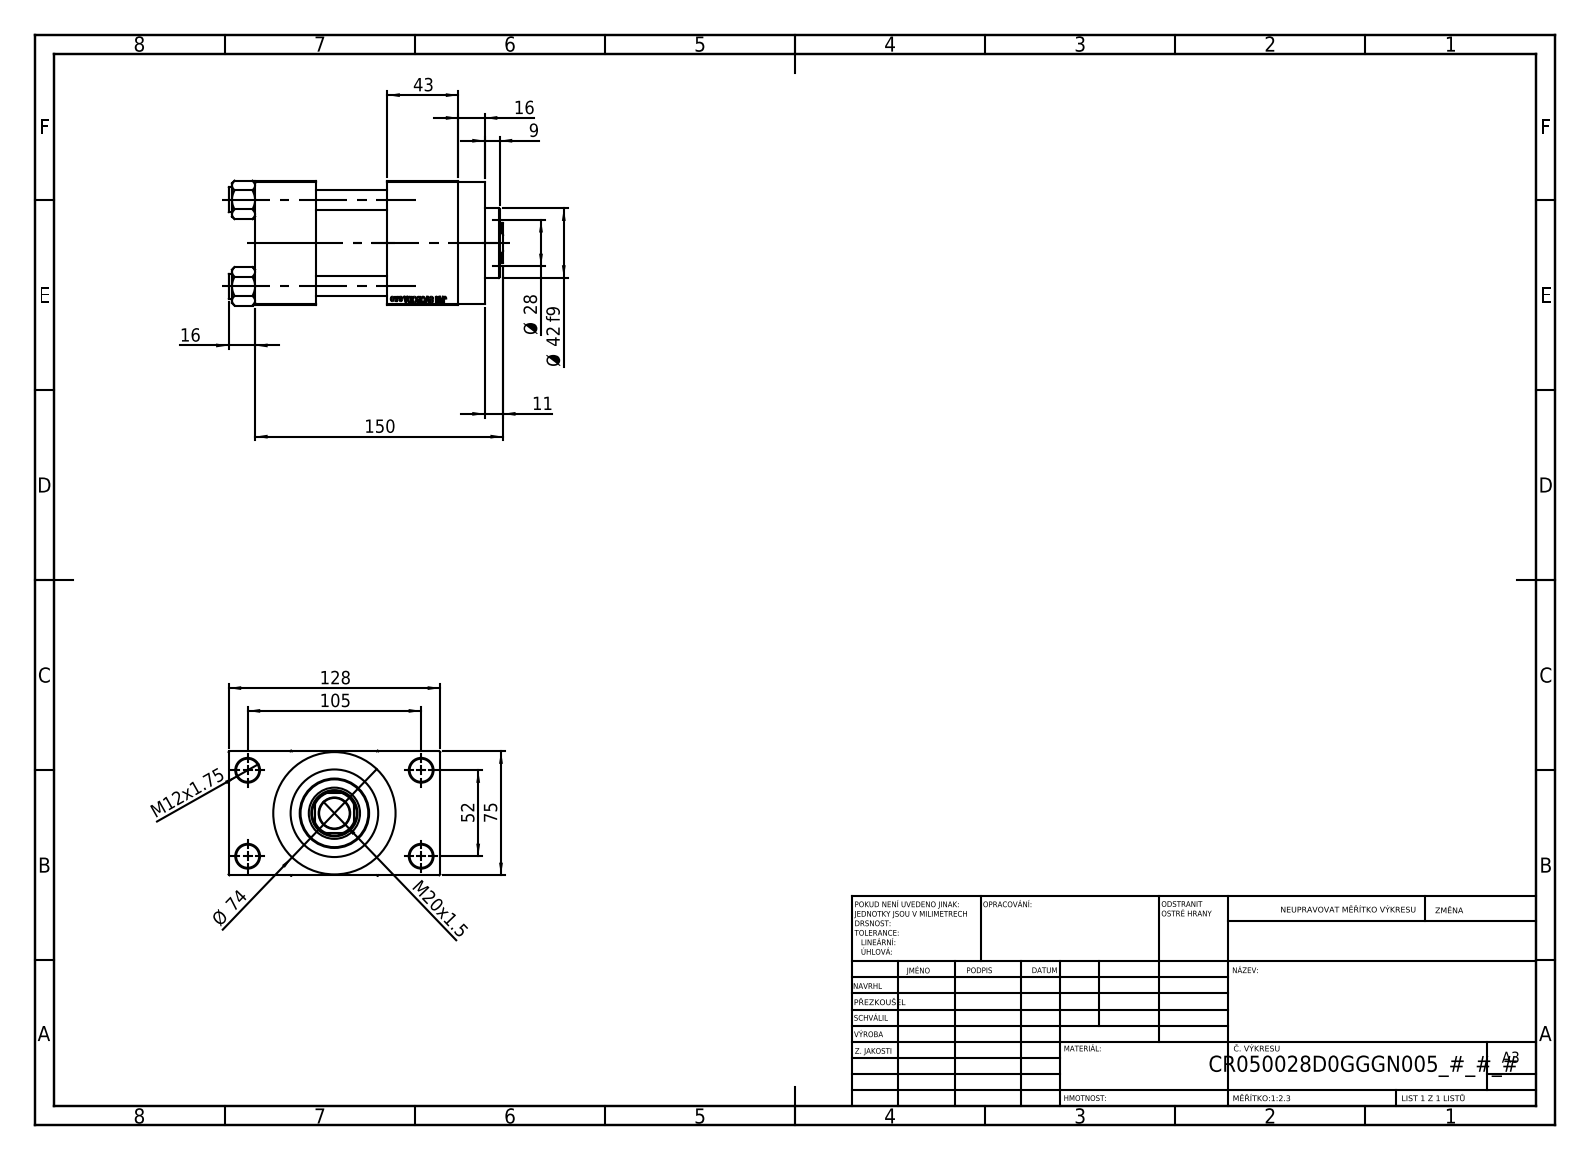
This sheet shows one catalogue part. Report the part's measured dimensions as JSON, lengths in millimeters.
{"part_name": "V215CR_VCP_D; V215CR_D_Body; NUT_M5_D; V215CR_D_TYCINKA (+1 more)", "step_written_by": "SolidWorks 2019 (CONFIG_CONTROL_DESIGN)", "units": "millimeters", "bodies": {"solids": 11, "faces": 1104, "planar": 497, "cylindrical": 89, "other": 518}, "overall_size": [166, 128, 75.54], "volume_mm3": 768271, "surface_area_mm2": 158300, "round_holes": [[12, 4], [14, 4], [7, 2], [20.96, 2], [30, 2], [18.5, 1], [28, 1], [31, 1], [41, 1], [50, 1], [53, 1]], "round_bosses_or_shafts": [[15, 4], [74, 1], [56, 1], [42, 1]], "partial_cylinders_radius": [[13.5, 1]], "face_to_face_distances": [43, 75, 80, 37, 26.5, 101.5, 86, 16, 123, 59], "hole_center_spacings": [26.35, 36.98, 52.3, 58.43, 58.59, 78.65, 94.37, 52]}
